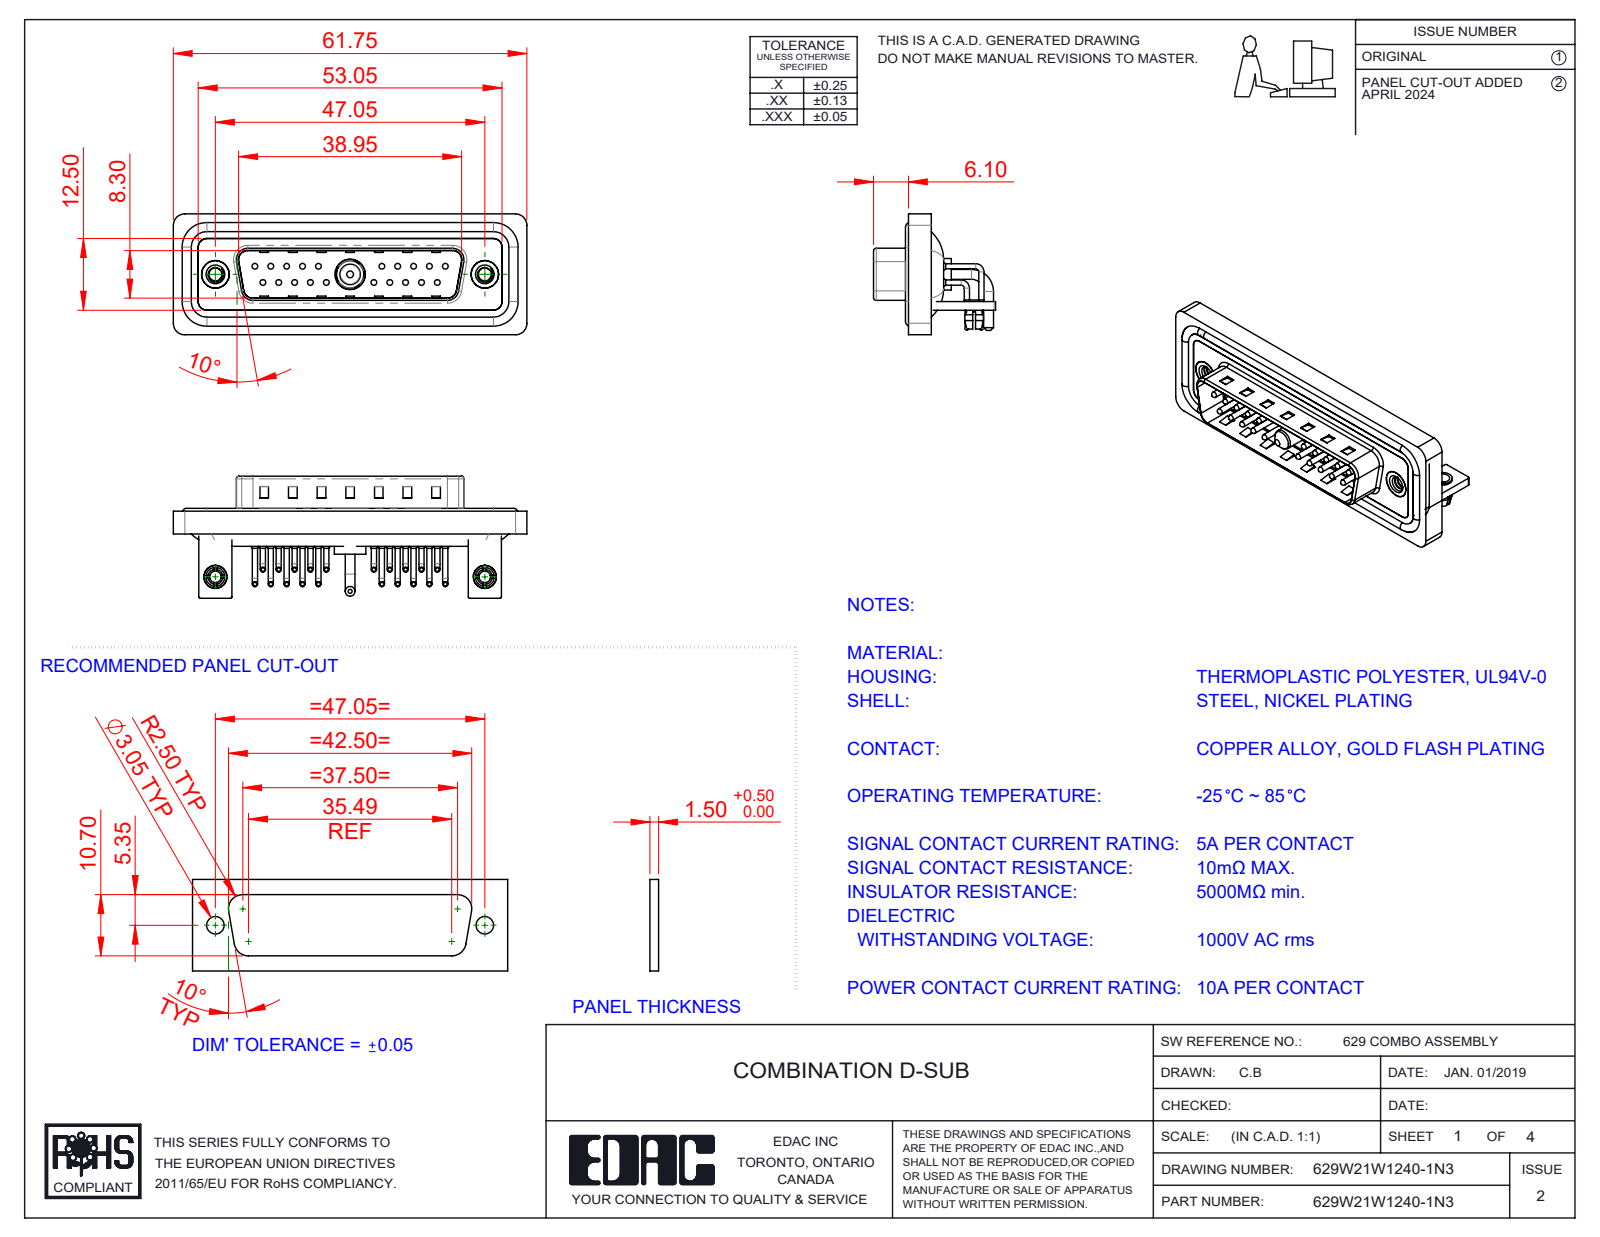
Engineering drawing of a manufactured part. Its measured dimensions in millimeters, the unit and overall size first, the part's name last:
Units: millimetres
Overall size (bounding box): 61.75 × 21.3 × 21.1
Round holes (diameter × count): ⌀2 ×22, ⌀0.75 ×20, ⌀1.6 ×20, ⌀2.26 ×2, ⌀2.5 ×2, ⌀3.2 ×2, ⌀4 ×2, ⌀4.8 ×2, ⌀5 ×2, ⌀4.85 ×1, ⌀5.3 ×1
Round bosses / shafts (diameter × count): ⌀0.9 ×40, ⌀1.5 ×20, ⌀1 ×20, ⌀0.65 ×20, ⌀1.6 ×4, ⌀4.9 ×2, ⌀4 ×2, ⌀3.4 ×2
Partial cylindrical surfaces — rounded edges, fillets, slot ends (radius × count): R1.01 ×20, R2 ×19, R1.5 ×18, R0.25 ×16, R0.5 ×9, R1.6 ×8, R0.6 ×4, R0.65 ×4
Main face-to-face distances: 0.4, 0.8, 2.1, 2.9, 1.5, 1.1, 4.1, 1.6, 4.5, 3.7
Hole centre spacings: 3.16, 2.77, 5.54, 8.31, 5.04, 19.39, 20.97, 22.16
Volume: 7 674 mm³ · Surface area: 13 467 mm²
Bodies: 33 solids, 2858 faces (1567 planar, 979 cylindrical, 312 other)
Part name (STEP PRODUCT): 629Combo Board Lock; 629Combo Shell Rear_25 Contacts; 629W21W1140-1N3; 629Combo Stabilizer Bracket (+7 more)
STEP written by: SolidWorks 2023 (CONFIG_CONTROL_DESIGN)
